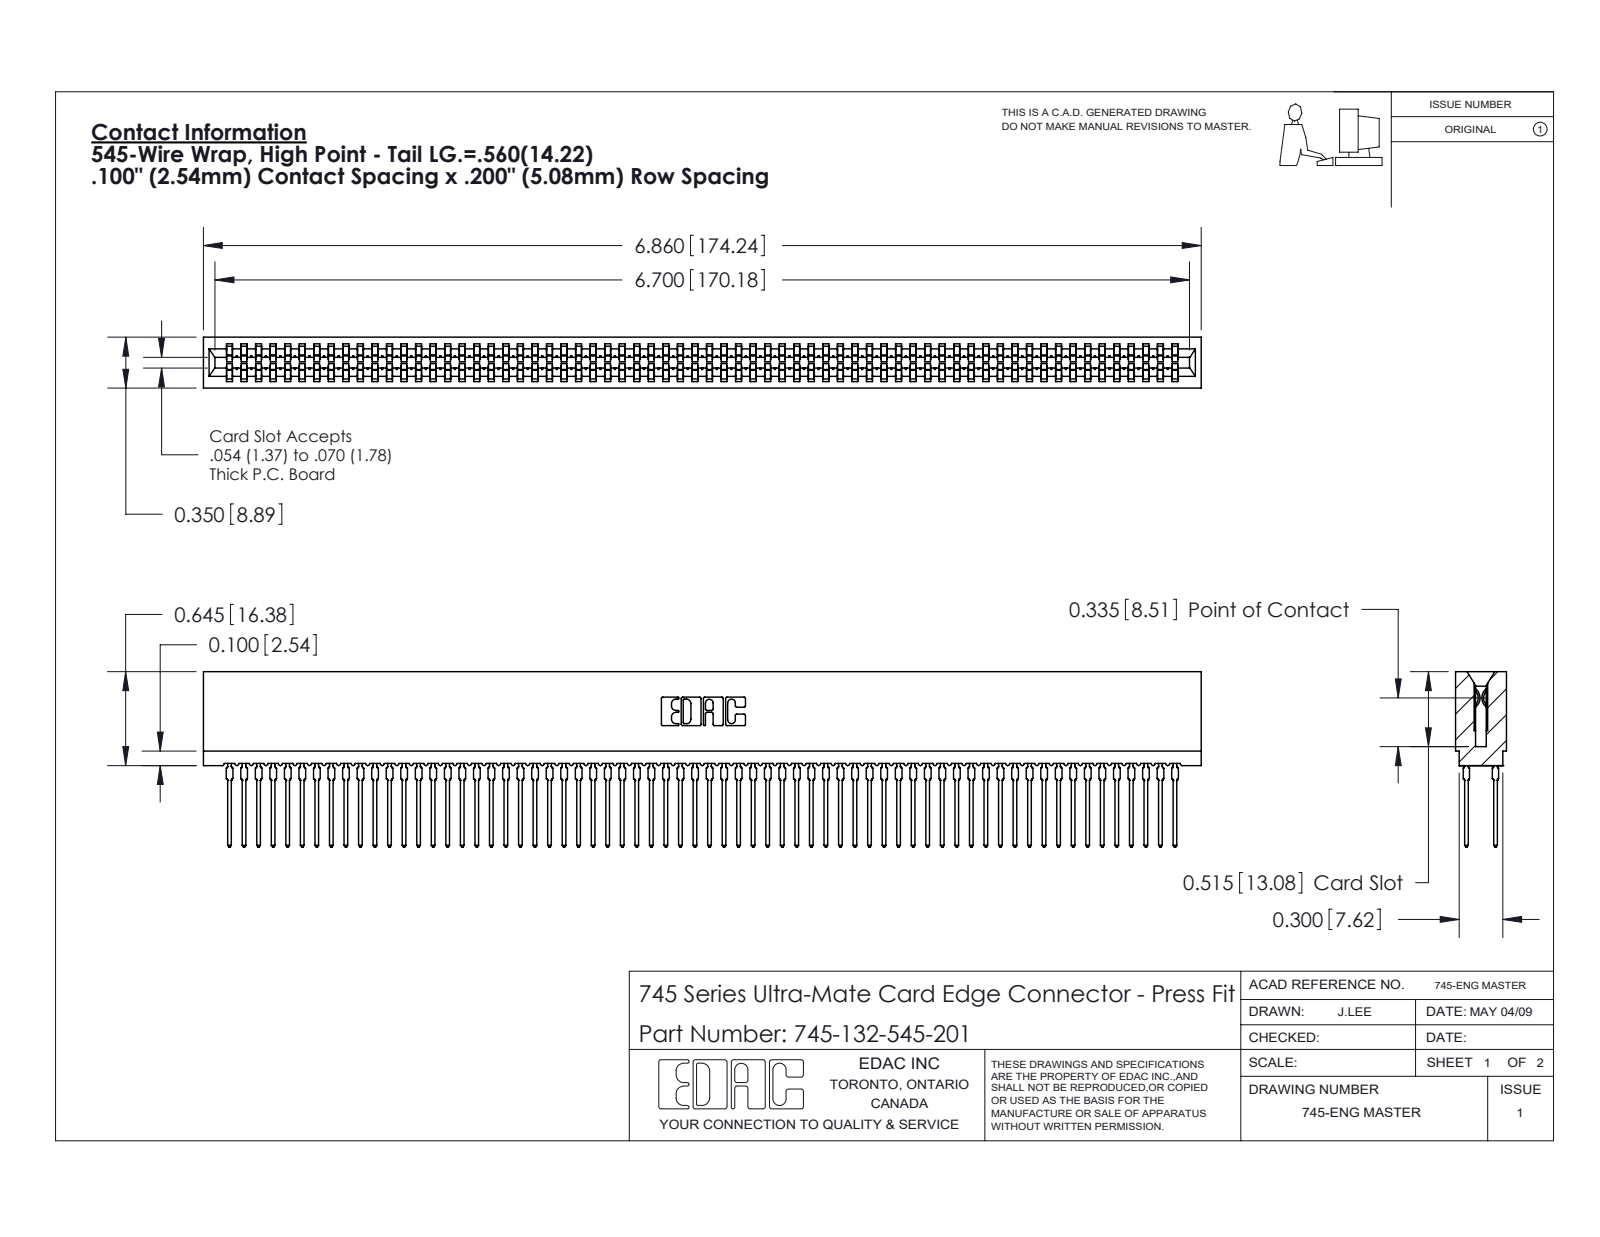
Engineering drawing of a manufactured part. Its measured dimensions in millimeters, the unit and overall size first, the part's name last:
Units: millimetres
Overall size (bounding box): 174.2 × 30.6 × 8.9
Partial cylindrical surfaces — rounded edges, fillets, slot ends (radius × count): R0.5 ×264, R0.4 ×132, R0.3 ×22, R0.1 ×8, R0.3 ×8, R0.2 ×6, R0.8 ×6, R0.7 ×3
Main face-to-face distances: 1.6, 7.3, 8.9, 5.1, 1.1, 7.7, 0.5, 6.2, 3.5, 5.4
Volume: 16 000 mm³ · Surface area: 35 120 mm²
Bodies: 133 solids, 11909 faces (6127 planar, 2350 cylindrical, 3432 other)
Part name (STEP PRODUCT): 745-132-545-201; 745 Part_Insulator Option - 01; 745-292-001_545
STEP written by: SolidWorks 2020 (CONFIG_CONTROL_DESIGN)
